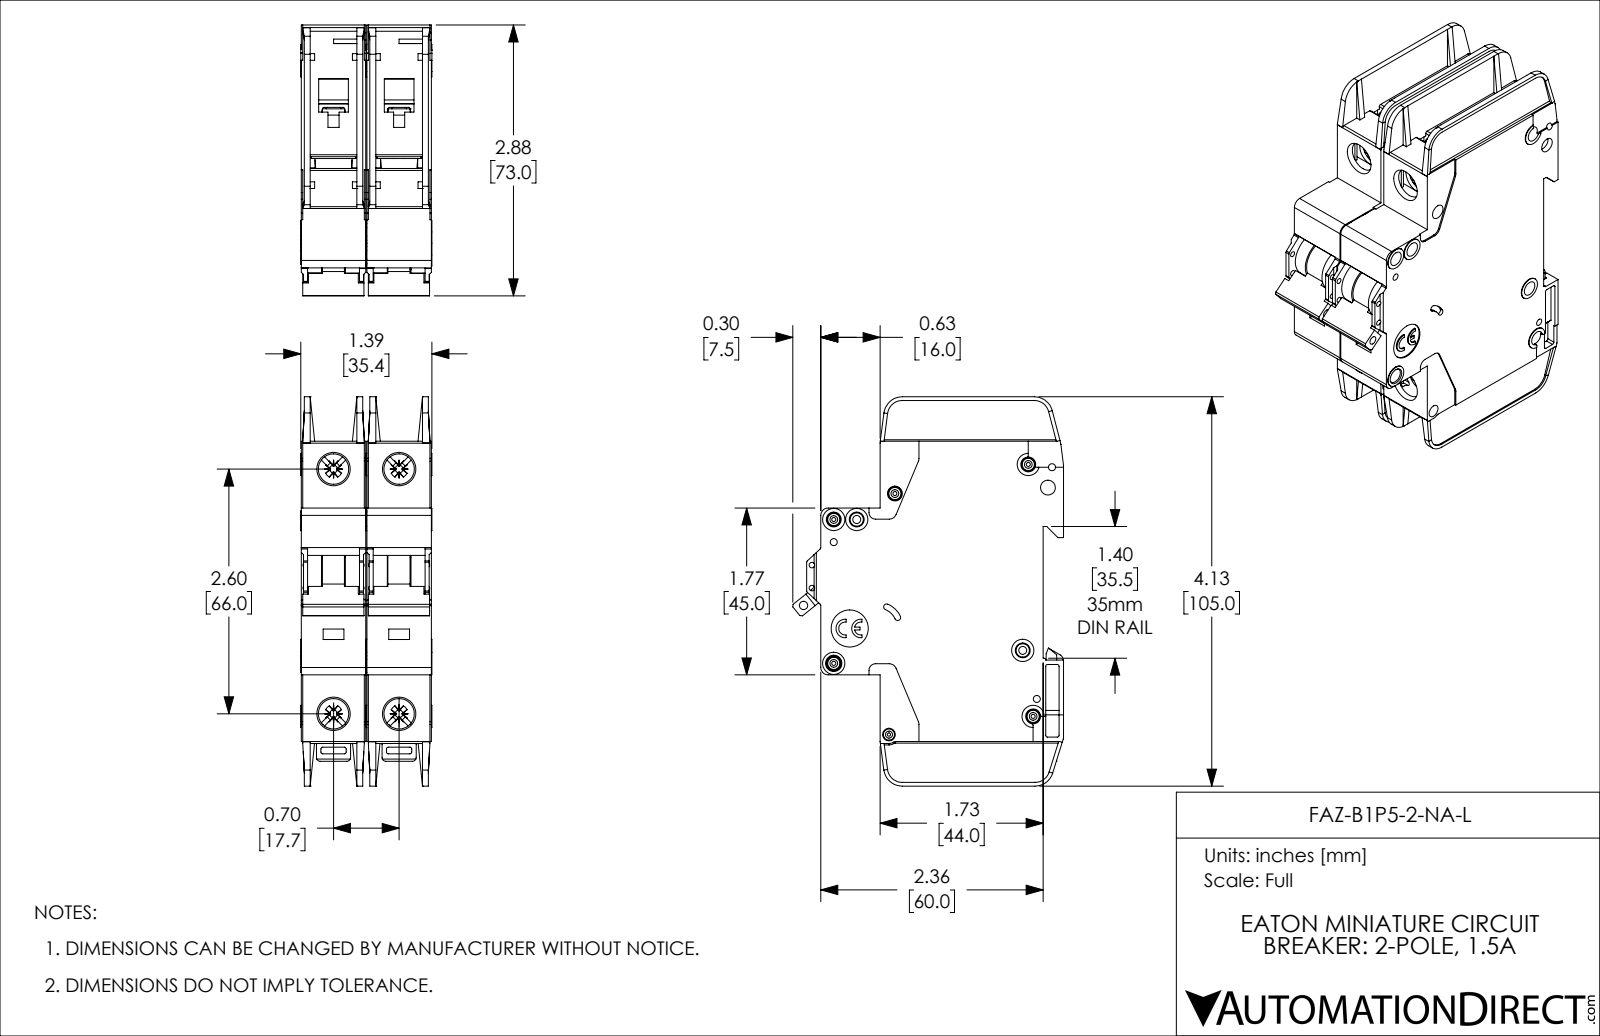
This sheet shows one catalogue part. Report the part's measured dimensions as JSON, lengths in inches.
{"part_name": "FAZ-B1P5-2-NA-L", "step_written_by": "SolidWorks 2019 (AUTOMOTIVE_DESIGN)", "units": "inches", "bodies": {"solids": 2, "faces": 2254, "planar": 1342, "cylindrical": 714, "other": 198}, "overall_size": [4.134, 2.876, 1.394], "volume_in3": 9.365, "surface_area_in2": 82.01, "round_holes": [[0.157, 8], [0.043, 5], [0.075, 4], [0.323, 4], [0.059, 2], [0.085, 2], [0.035, 1], [0.089, 1], [0.098, 1], [0.134, 1], [0.394, 1]], "round_bosses_or_shafts": [[0.13, 5], [0.236, 4], [0.118, 3], [0.098, 2]], "partial_cylinders_radius": [[0.02, 57], [0.016, 20], [0.039, 14], [0.079, 10], [0.043, 8], [0.008, 5], [0.197, 5], [0.01, 4]], "face_to_face_distances": [0.697, 0.047, 0.685, 0.591, 0.094, 0.638, 0.543, 1.382, 0.744, 0.65], "hole_center_spacings": [0.244, 0.537, 0.697, 0.87, 2.598, 2.69, 0.189, 0.199]}
